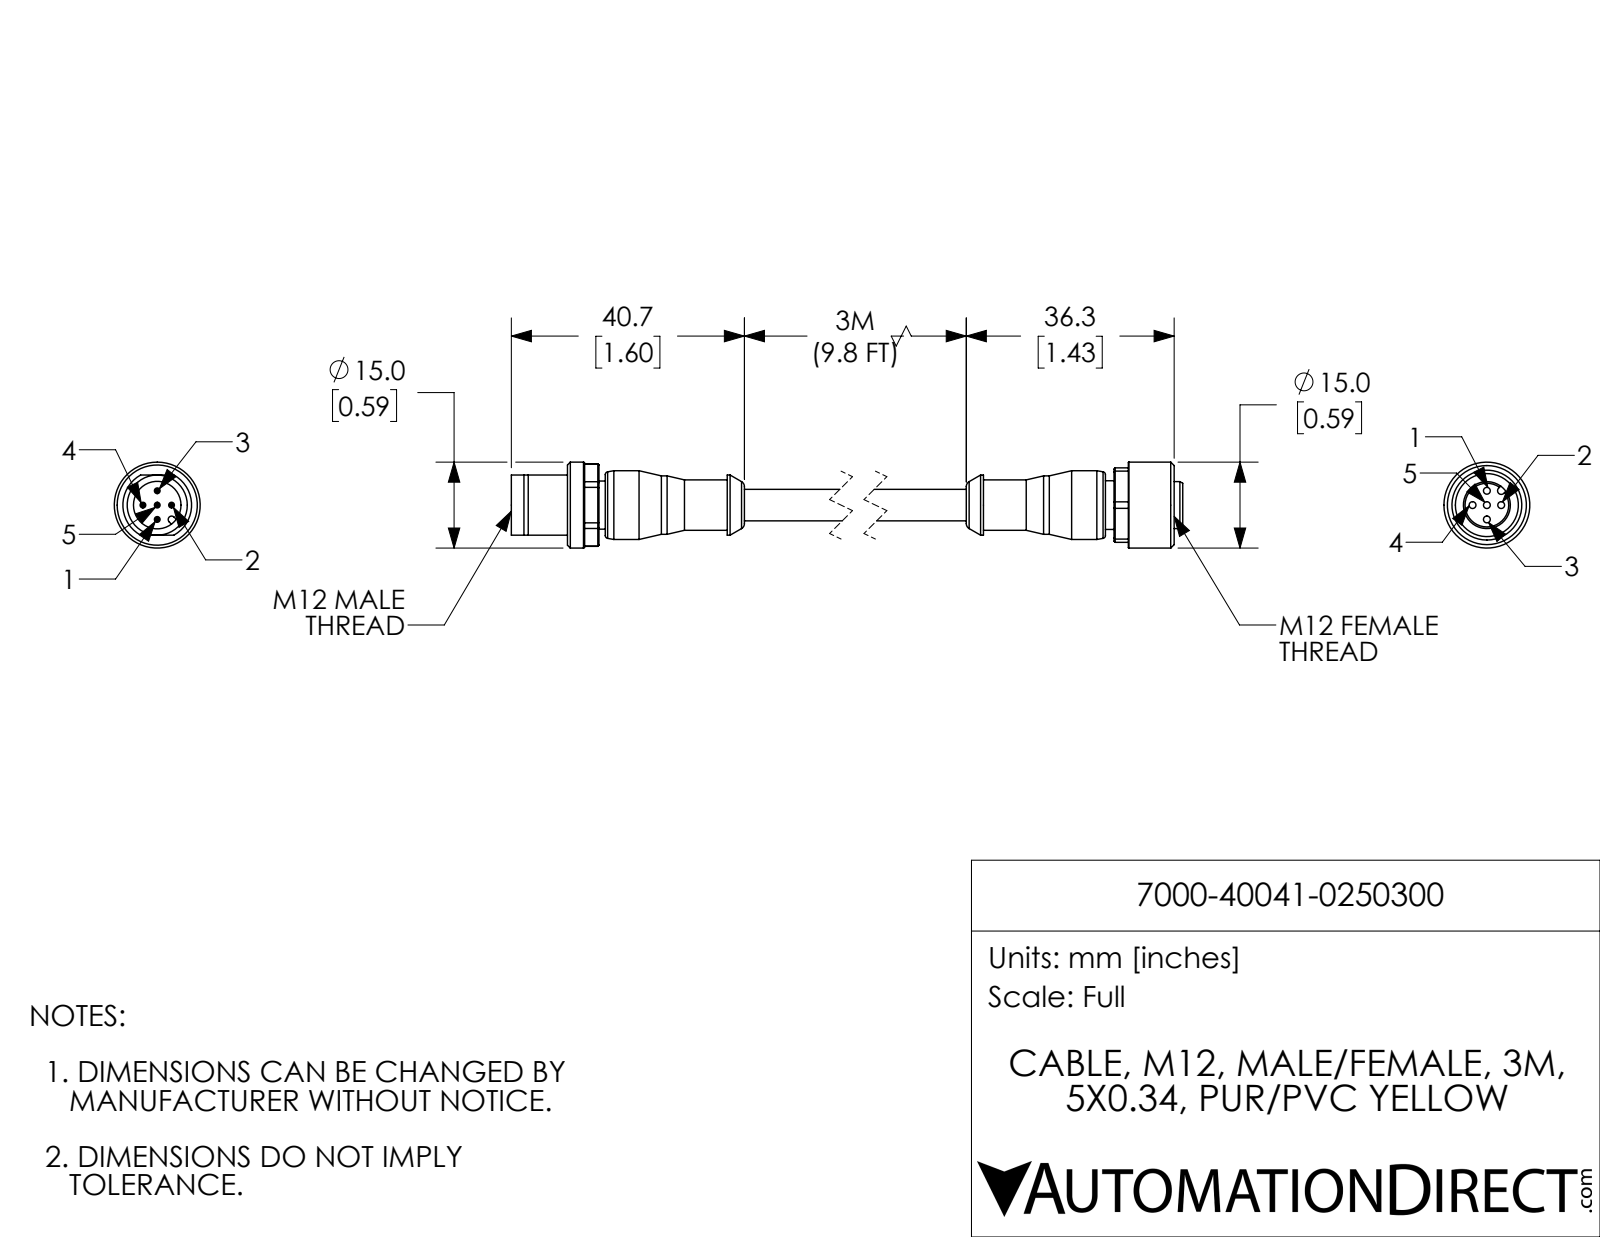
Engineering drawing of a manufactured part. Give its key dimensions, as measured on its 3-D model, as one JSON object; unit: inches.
{"part_name": "7000-40041-0250300_MALE; 7000-40041-0250300; 7000-40041-0250300_FEMALE", "step_written_by": "SolidWorks 2017 (AUTOMOTIVE_DESIGN)", "units": "inches", "bodies": {"solids": 2, "faces": 196, "planar": 60, "cylindrical": 73, "other": 63}, "overall_size": [5.138, 0.591, 0.591], "volume_in3": 0.488, "surface_area_in2": 8.004, "round_holes": [[0.047, 5], [0.327, 1], [0.433, 1]], "round_bosses_or_shafts": [[0.039, 5], [0.591, 1], [0.472, 1], [0.413, 1], [0.402, 1], [0.346, 1], [0.335, 1], [0.331, 1]], "partial_cylinders_radius": [[0.024, 1], [0.026, 1], [0.283, 1]], "face_to_face_distances": [0.472, 0.512, 0.118, 4.063, 0.413, 4.433, 2.217, 4.28, 0.295, 0.059], "hole_center_spacings": [0.098, 0.139, 0.197]}
